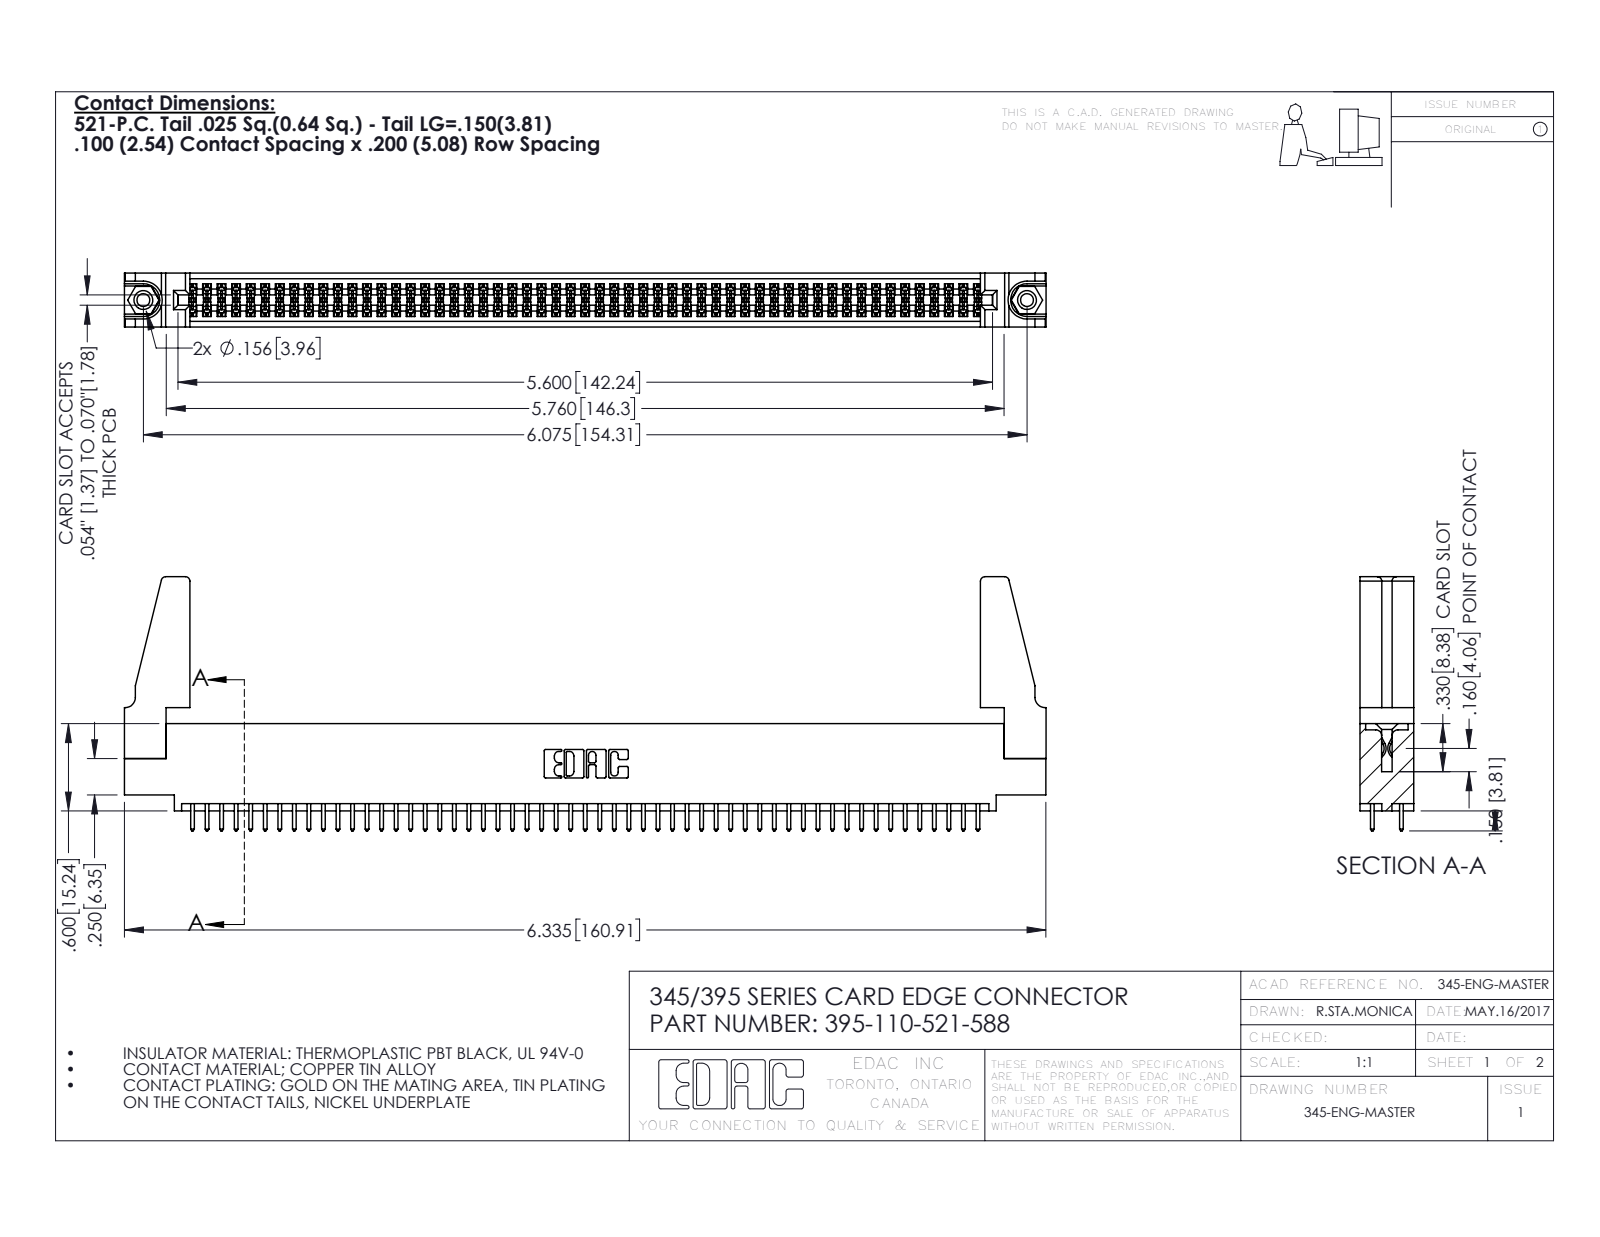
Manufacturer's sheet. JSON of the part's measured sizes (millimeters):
{"part_name": "395-110-521-588; 345-250-001_345-250-001-102; 345-220-078_345-220-088; 345-292-001_345-293-121 (+1 more)", "step_written_by": "SolidWorks 2016 (CONFIG_CONTROL_DESIGN)", "units": "millimeters", "bodies": {"solids": 115, "faces": 5754, "planar": 3786, "cylindrical": 1952, "other": 16}, "overall_size": [160.9, 44.4, 9.4], "volume_mm3": 18890, "surface_area_mm2": 26280, "round_holes": [[2.3, 2], [3.2, 2], [4, 2], [1.6, 1]], "round_bosses_or_shafts": [[3.9, 2]], "partial_cylinders_radius": [[0.2, 165], [0.3, 110], [0.3, 22], [0.8, 8], [0.2, 6], [0.8, 6], [0.7, 3], [0.4, 2]], "face_to_face_distances": [1.8, 7.6, 9.4, 5.1, 2.5, 6.9, 0.6, 5.7, 4.4, 3.8], "hole_center_spacings": [6.9, 148.3, 154.3]}
